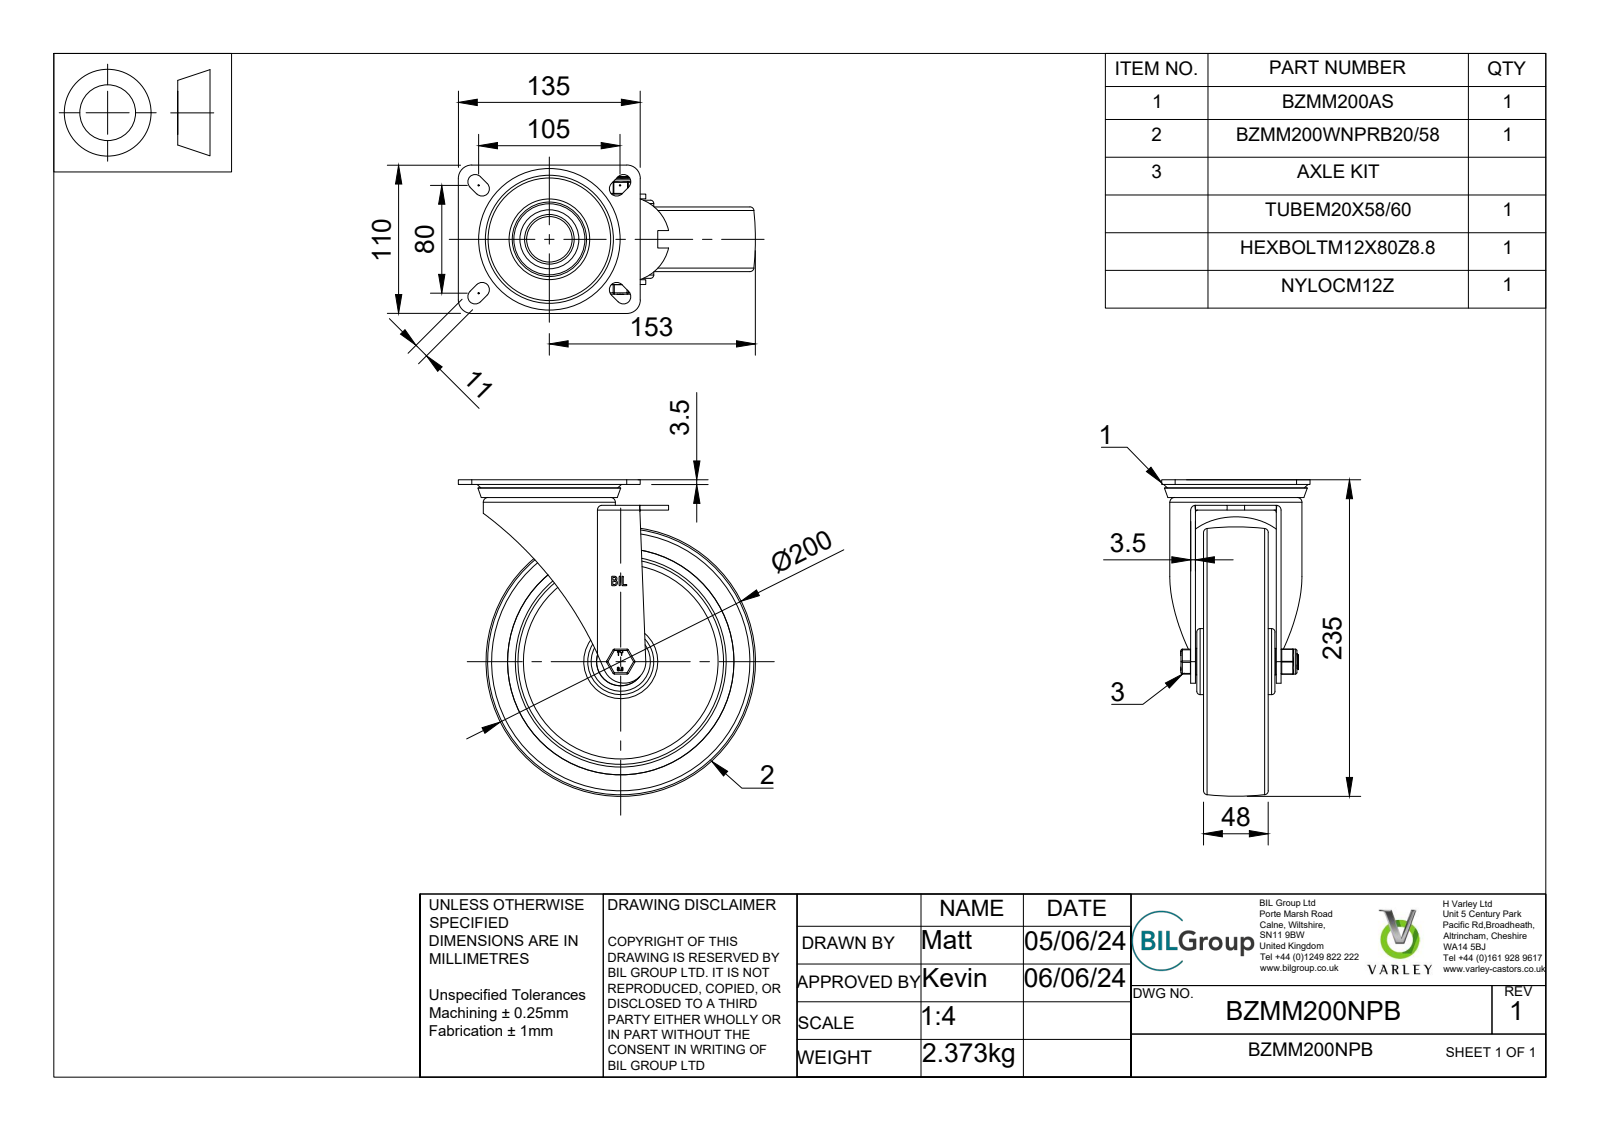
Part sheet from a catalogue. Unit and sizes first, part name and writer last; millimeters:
Units: millimetres
Overall size (bounding box): 235 × 220.5 × 110
Round holes (diameter × count): ⌀12 ×1, ⌀12.2 ×1, ⌀14 ×1, ⌀20 ×1, ⌀20.5 ×1, ⌀30 ×1, ⌀33.75 ×1, ⌀36 ×1, ⌀55 ×1, ⌀91 ×1, ⌀152.5 ×1, ⌀168 ×1
Round bosses / shafts (diameter × count): ⌀5 ×10, ⌀98 ×1, ⌀78 ×1, ⌀50 ×1, ⌀49 ×1, ⌀39.75 ×1, ⌀35.8 ×1, ⌀29.5 ×1
Partial cylindrical surfaces — rounded edges, fillets, slot ends (radius × count): R0.5 ×18, R1 ×12, R5.5 ×8, R1.75 ×4, R10 ×4, R3.5 ×2, R32.45 ×2, R12.5 ×1
Main face-to-face distances: 27, 6, 21, 3.5, 54, 48, 33, 9.5, 30.5, 36.5
Volume: 1 002 000 mm³ · Surface area: 308 032 mm²
Bodies: 61 solids, 548 faces (245 planar, 158 cylindrical, 145 other)
Part name (STEP PRODUCT): BZMM200NPB v4; BZMM200AS - 2 v2; ZINC PLATED, PRESSED STEEL TOP PLATE; ZINC PLATED, PRESSED STEEL TOP PLATE Geometry (+7 more)
STEP written by: Autodesk Translation Framework v13.14.0.145 (AUTOMOTIVE_DESIGN)
